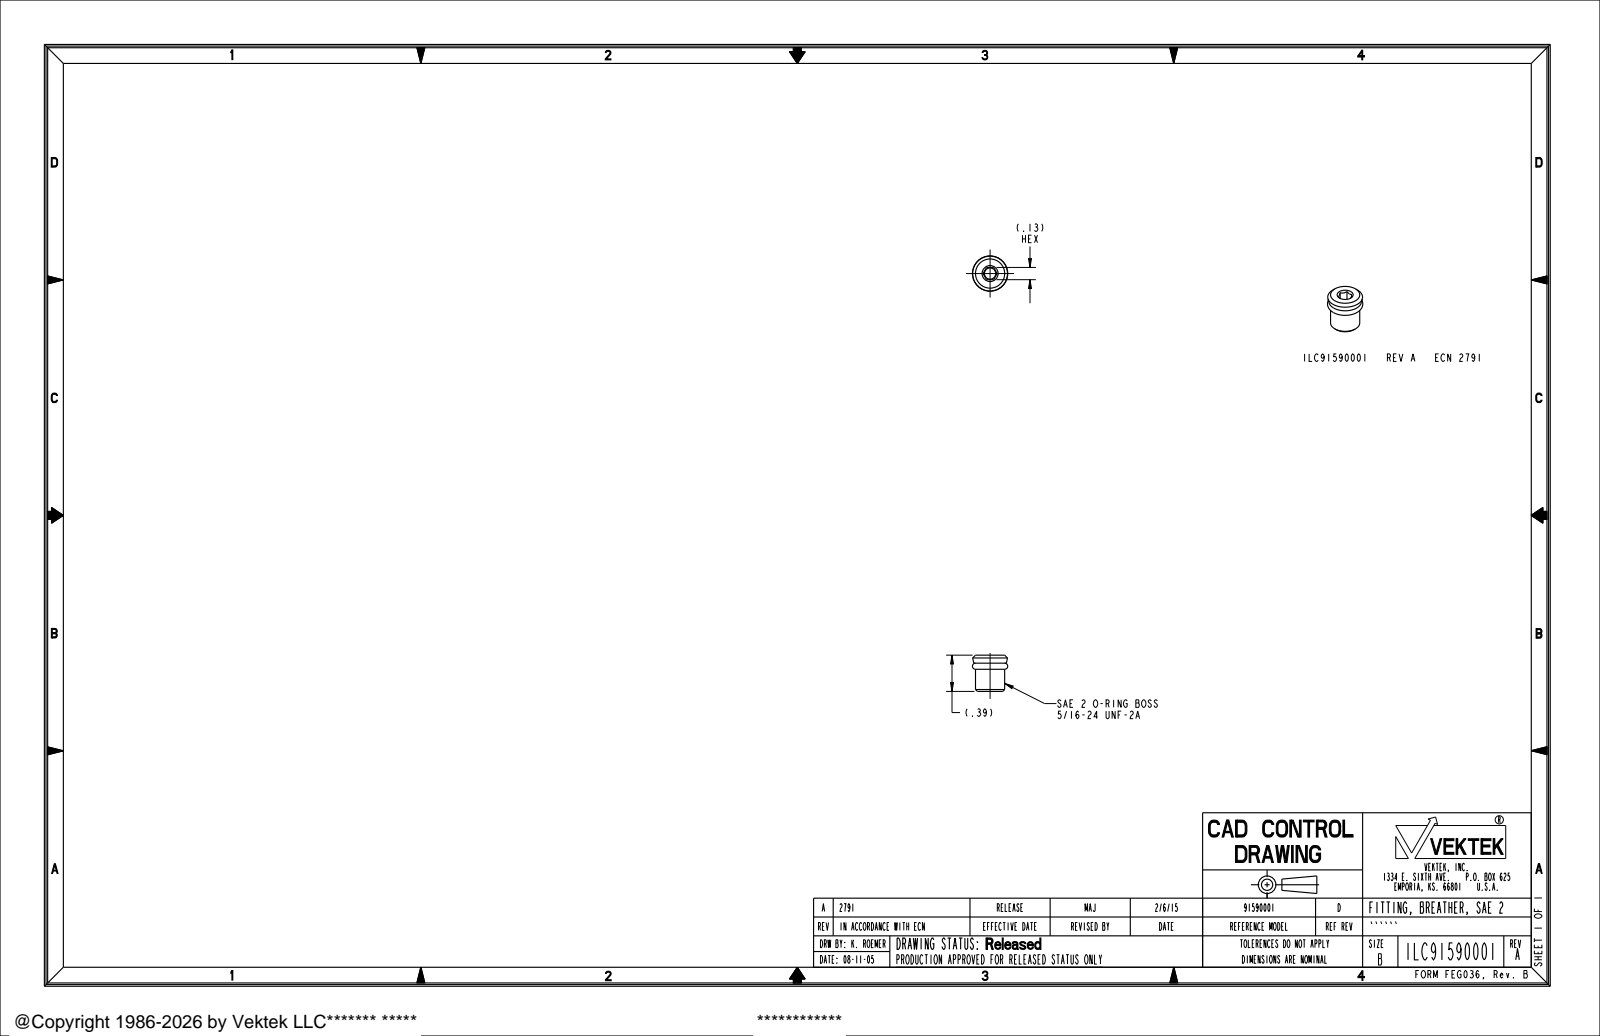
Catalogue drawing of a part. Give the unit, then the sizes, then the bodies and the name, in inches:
Units: inches
Overall size (bounding box): 0.385 × 0.375 × 0.375
Round holes (diameter × count): ⌀0.12 ×1
Round bosses / shafts (diameter × count): ⌀0.31 ×1
Main face-to-face distances: 0.385, 0.13, 0.3, 0.085, 0.193, 0.107, 0.192, 0.188, 0.295, 0.38
Volume: 0.03 in³ · Surface area: 0.689 in²
Bodies: 1 solid, 28 faces (12 planar, 6 cylindrical, 10 other)
Part name (STEP PRODUCT): ILC91590001
STEP written by: PRO/ENGINEER BY PARAMETRIC TECHNOLOGY CORPORATION, 2013320 (CONFIG_CONTROL_DESIGN)
